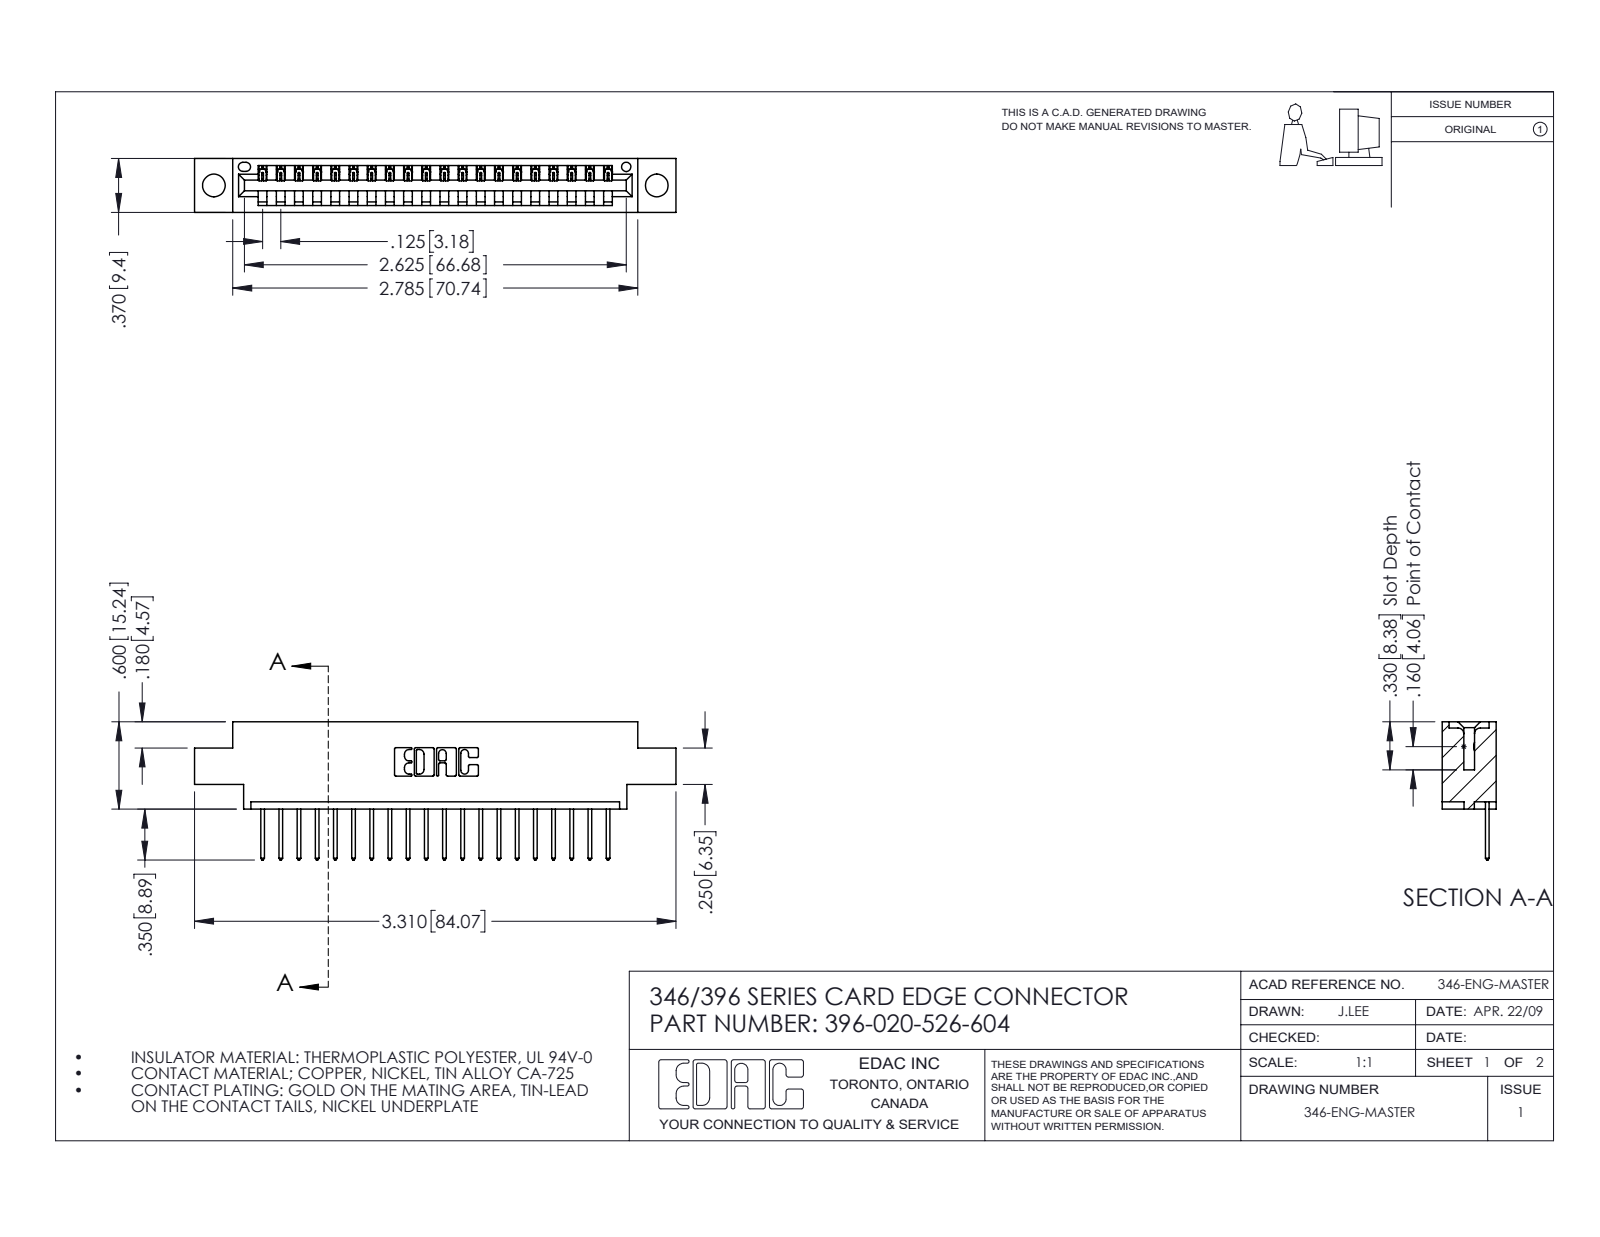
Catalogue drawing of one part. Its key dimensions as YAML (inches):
part_name: "396-020-526-604; 345-292-001_345-293-126; 346 Part_0.170 Offset - 0.156 Dia-TH"
step_written_by: "SolidWorks 2016 (CONFIG_CONTROL_DESIGN)"
units: inches
bodies: {solids: 21, faces: 1286, planar: 880, cylindrical: 406, other: 0}
overall_size: [3.31, 0.95, 0.37]
volume: 0.466
surface_area: 14.34
round_holes:
  - {diameter: 0.156, count: 2}
  - {diameter: 0.064, count: 1}
partial_cylinders:
  - {radius: 0.006, count: 40}
  - {radius: 0.01, count: 40}
  - {radius: 0.01, count: 22}
  - {radius: 0.007, count: 6}
  - {radius: 0.031, count: 6}
  - {radius: 0.026, count: 3}
  - {radius: 0.031, count: 2}
  - {radius: 0.04, count: 2}
face_to_face_distances: [0.048, 0.322, 0.37, 0.25, 0.072, 0.298, 0.025, 0.148, 0.222, 0.1]
hole_center_spacings: [0.246, 2.837, 3.045]
